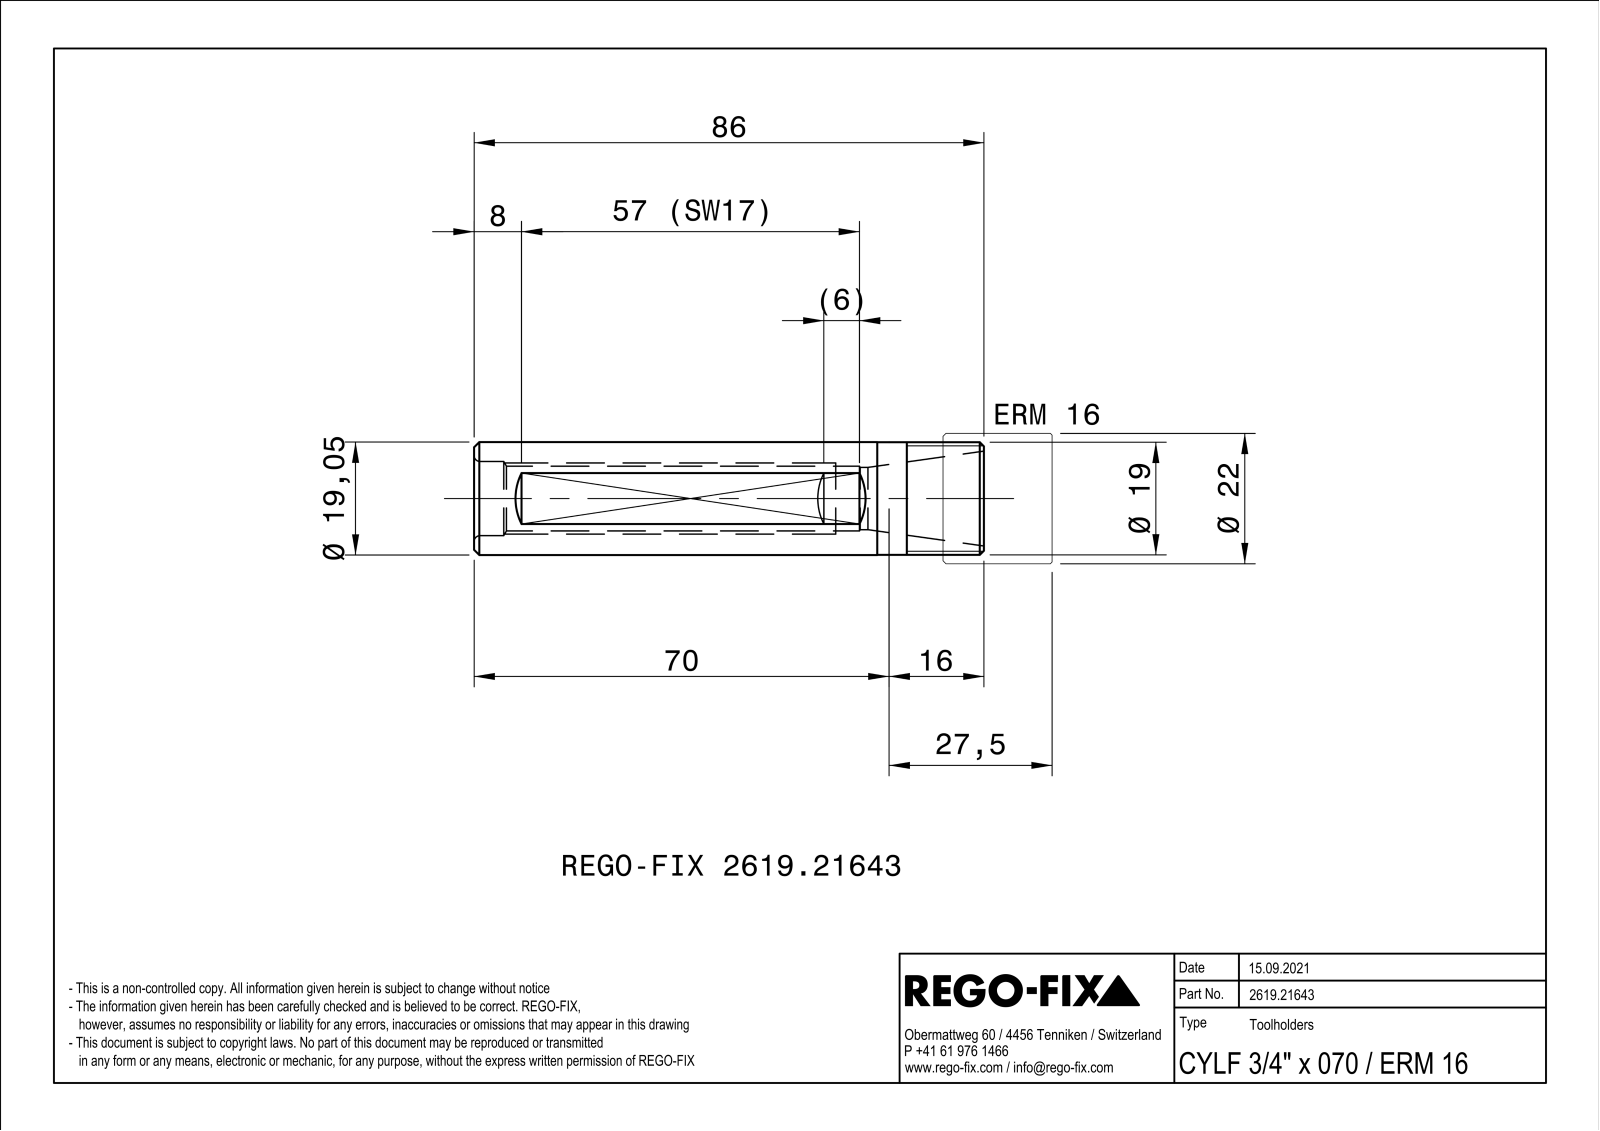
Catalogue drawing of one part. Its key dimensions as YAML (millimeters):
part_name: "NOCUT"
step_written_by: "SIEMENS PLM Software Solid Edge ST10 (AUTOMOTIVE_DESIGN)"
units: millimeters
bodies: {solids: 2, faces: 44, planar: 18, cylindrical: 12, other: 14}
overall_size: [86.2, 19.3, 19.3]
volume: 30668
surface_area: 16981
round_holes:
  - {diameter: 10.5, count: 1}
  - {diameter: 10.92, count: 1}
  - {diameter: 12.5, count: 1}
round_bosses_or_shafts:
  - {diameter: 19.3, count: 1}
  - {diameter: 19.05, count: 1}
  - {diameter: 19, count: 1}
face_to_face_distances: [17, 86.2, 86, 28.28, 7.78, 18, 1, 16.2, 16, 70]
